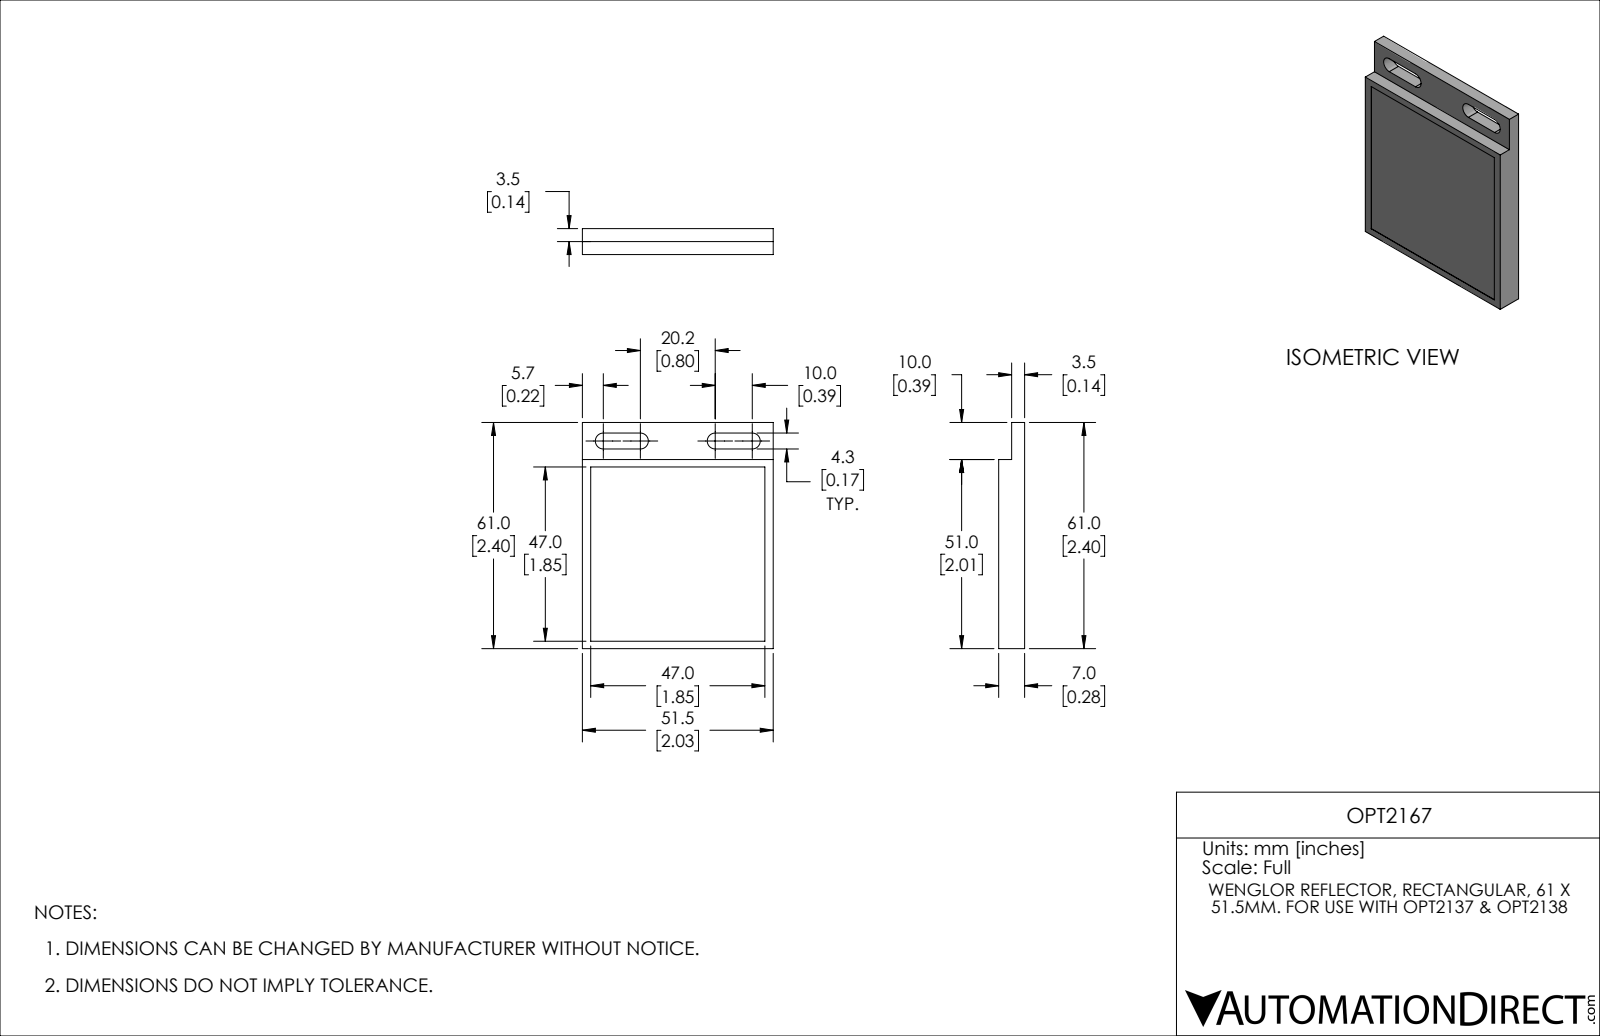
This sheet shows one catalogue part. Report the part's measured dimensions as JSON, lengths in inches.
{"part_name": "OPT2167", "step_written_by": "SolidWorks 2019 (AUTOMOTIVE_DESIGN)", "units": "inches", "bodies": {"solids": 1, "faces": 21, "planar": 17, "cylindrical": 4, "other": 0}, "overall_size": [2.402, 2.028, 0.276], "volume_in3": 1.194, "surface_area_in2": 12.11, "partial_cylinders_radius": [[0.085, 4]], "face_to_face_distances": [0.272, 0.138, 0.276, 0.134, 2.028, 2.008, 2.402, 0.394, 0.112, 0.281]}
